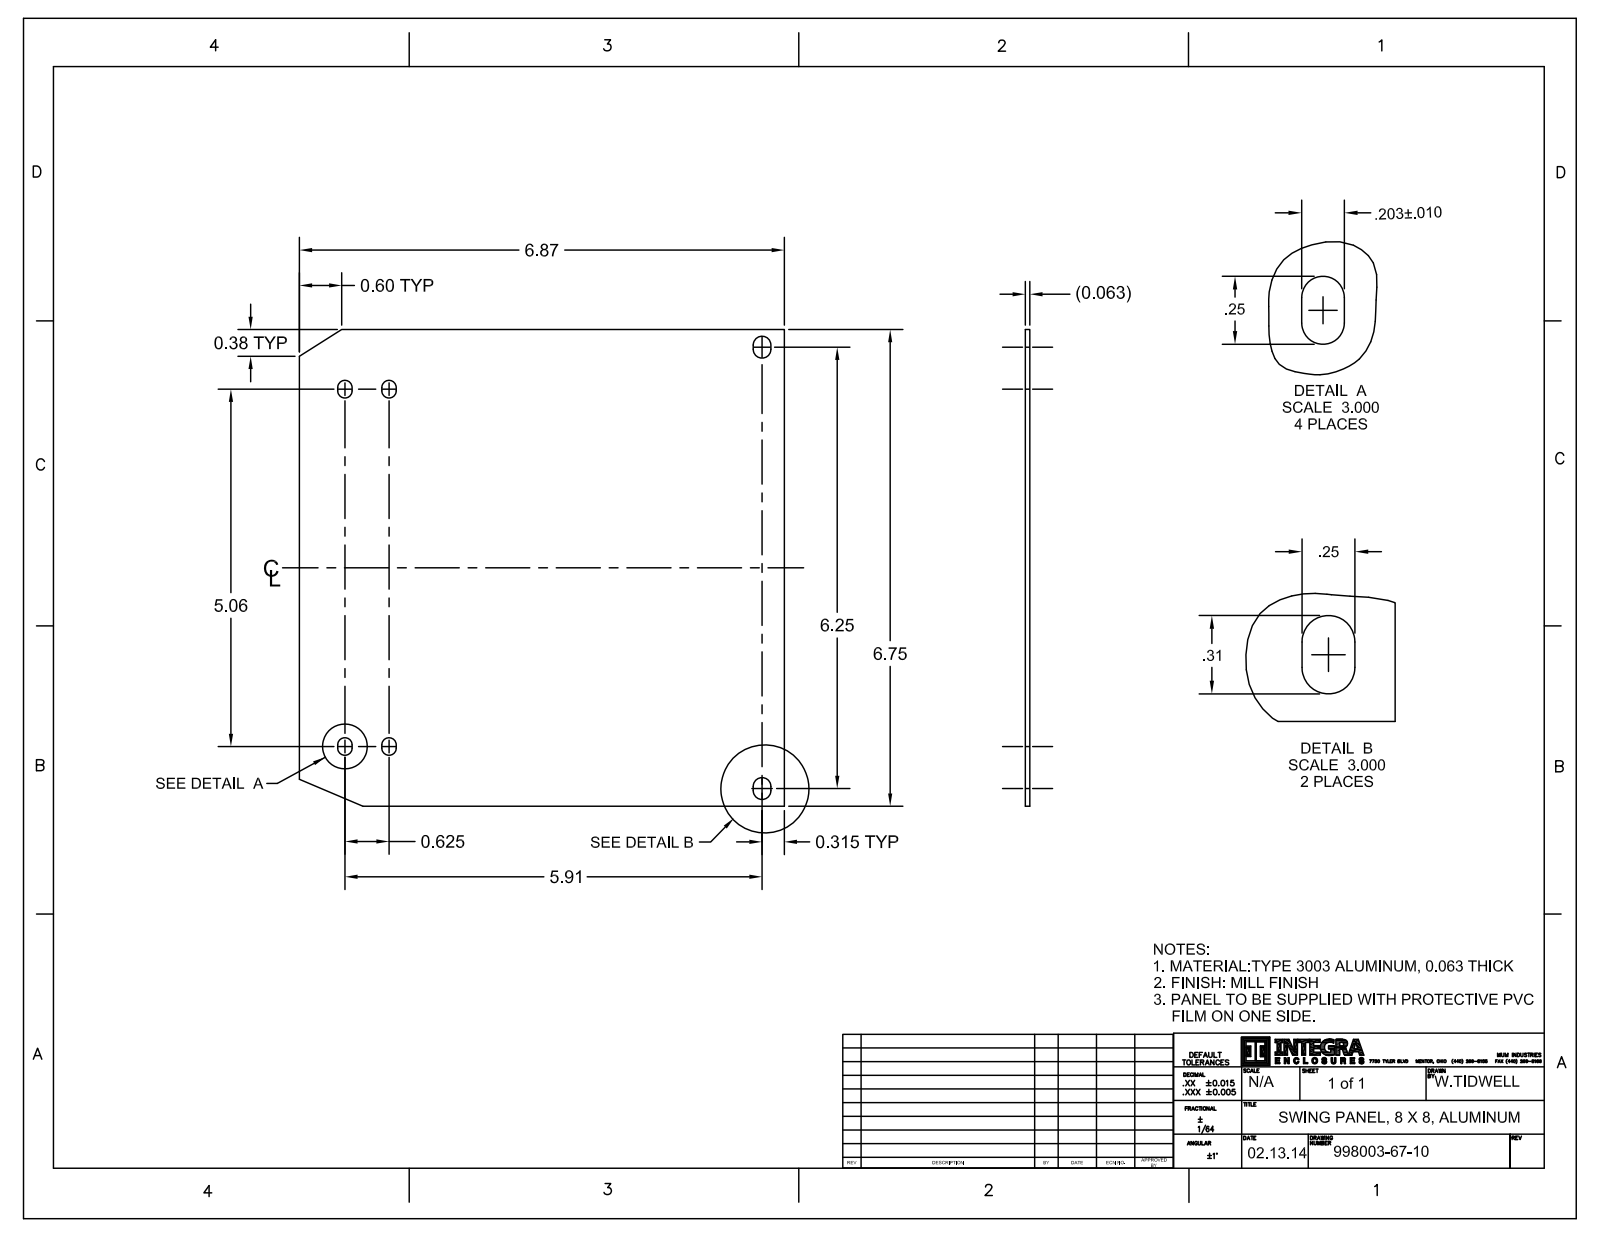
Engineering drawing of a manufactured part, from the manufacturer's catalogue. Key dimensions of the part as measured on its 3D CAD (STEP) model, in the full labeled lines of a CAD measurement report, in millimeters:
Part name (STEP PRODUCT): 9912511-20-50; 9912525-80-10; 9912511-20-50_ASM; 995008-20-90 (+8 more)
STEP written by: CREO PARAMETRIC BY PTC INC, 2016050 (CONFIG_CONTROL_DESIGN)
Units: millimetres
Bodies: 31 solids, 2116 faces (478 planar, 994 cylindrical, 644 other)
Overall size (bounding box): 196.3 × 196.3 × 40.9
Volume: 96 650 mm³ · Surface area: 93 100 mm²
Round holes (diameter × count): ⌀4.8 ×8, ⌀6.2 ×8, ⌀9.1 ×8, ⌀5.3 ×4, ⌀8 ×4, ⌀6.9 ×2
Round bosses / shafts (diameter × count): ⌀6.4 ×12, ⌀7.6 ×8, ⌀7.6 ×8, ⌀7.4 ×8, ⌀6.6 ×8, ⌀6.6 ×8, ⌀11.2 ×6, ⌀10.9 ×6
Partial cylindrical surfaces — rounded edges, fillets, slot ends (radius × count): R0.8 ×120, R0.1 ×48, R0.1 ×42, R1.3 ×36, R0.7 ×16, R1.2 ×16, R1.5 ×16, R0.5 ×12
Main face-to-face distances: 1.6, 129, 1.2, 12.7, 9.7, 2.8, 119.6, 141.7, 2.8, 30.5
Hole centre spacings: 2.8, 158.8, 158.8, 15.9, 17.2, 28.7, 129, 130
